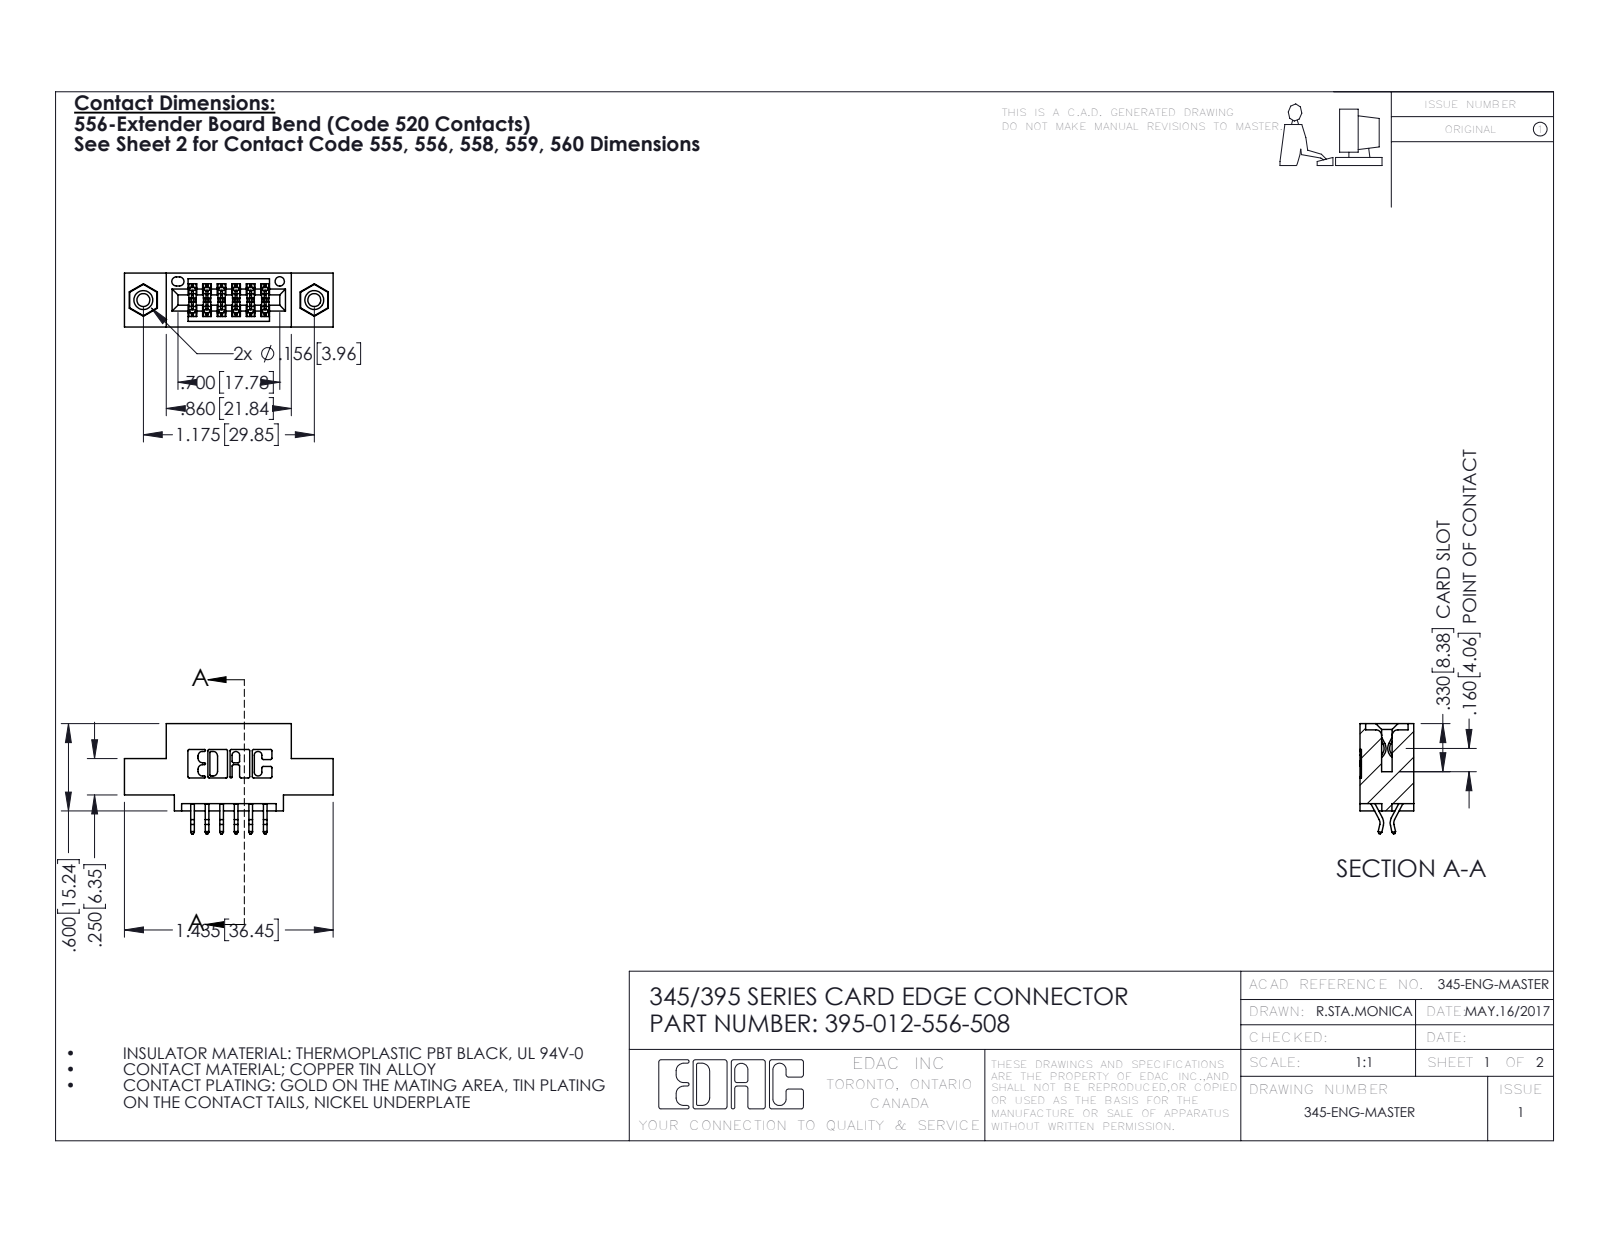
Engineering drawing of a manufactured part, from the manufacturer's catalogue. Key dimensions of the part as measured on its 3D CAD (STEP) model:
Part name (STEP PRODUCT): 345-292-001_556 Tail; 345 Part_0.110 Offset - 0.156 Dia-TI; 345-250-001_345-250-003-102; 395-012-556-508
STEP written by: SolidWorks 2016 (CONFIG_CONTROL_DESIGN)
Units: inches
Bodies: 15 solids, 862 faces (560 planar, 286 cylindrical, 16 other)
Overall size (bounding box): 1.435 × 0.757 × 0.37
Volume: 0.191 in³ · Surface area: 6.23 in²
Round holes (diameter × count): ⌀0.089 ×2, ⌀0.125 ×2, ⌀0.156 ×2, ⌀0.064 ×1
Round bosses / shafts (diameter × count): ⌀0.155 ×2
Partial cylindrical surfaces — rounded edges, fillets, slot ends (radius × count): R0.01 ×22, R0.006 ×18, R0.007 ×6, R0.031 ×6, R0.026 ×3, R0.01 ×2, R0.014 ×2, R0.019 ×2
Main face-to-face distances: 0.2, 0.37, 0.072, 0.298, 0.1, 0.025, 0.098, 0.272, 0.16, 0.06
Hole centre spacings: 0.27, 0.946, 1.175
